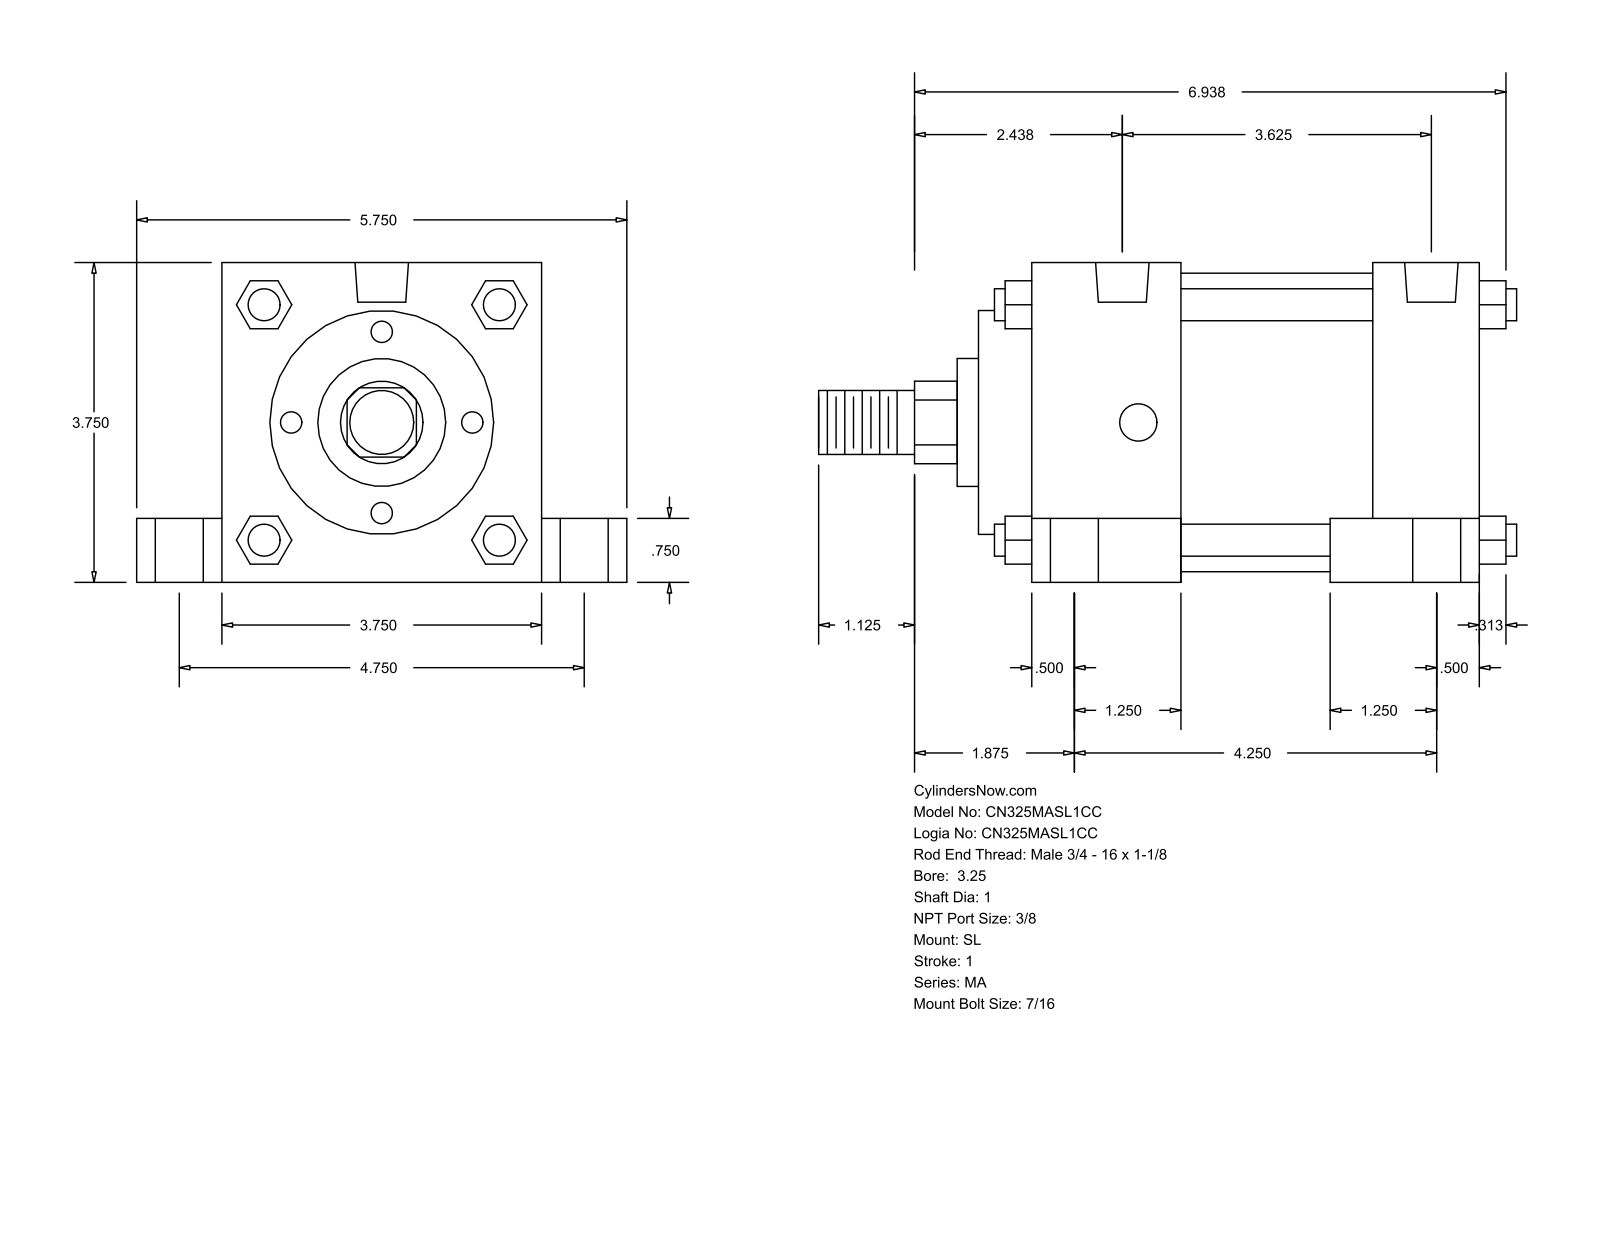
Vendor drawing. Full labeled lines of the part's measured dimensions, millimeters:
Part name (STEP PRODUCT): MA_SL__0325_1
STEP written by: GSSL Pune (CONFIG_CONTROL_DESIGN)
Units: millimetres
Bodies: 0 solids, 150 faces (113 planar, 37 cylindrical, 0 other)
Overall size (bounding box): 207.96 × 146.05 × 95.25
Round holes (diameter × count): ⌀11.11 ×4, ⌀14.29 ×4, ⌀20.64 ×4, ⌀15.93 ×2
Round bosses / shafts (diameter × count): ⌀9.53 ×4, ⌀88.9 ×1, ⌀66.67 ×1, ⌀38.1 ×1, ⌀25.4 ×1, ⌀19.05 ×1
Partial cylindrical surfaces — rounded edges, fillets, slot ends (radius × count): R12.29 ×1
Main face-to-face distances: 95.24, 133.36, 57.15, 15.87, 25.41, 120.65, 19.05, 101.61, 31.75, 44.46
Hole centre spacings: 60.35, 60.66, 62, 63.27, 82.55, 107.44, 107.95, 111.41
